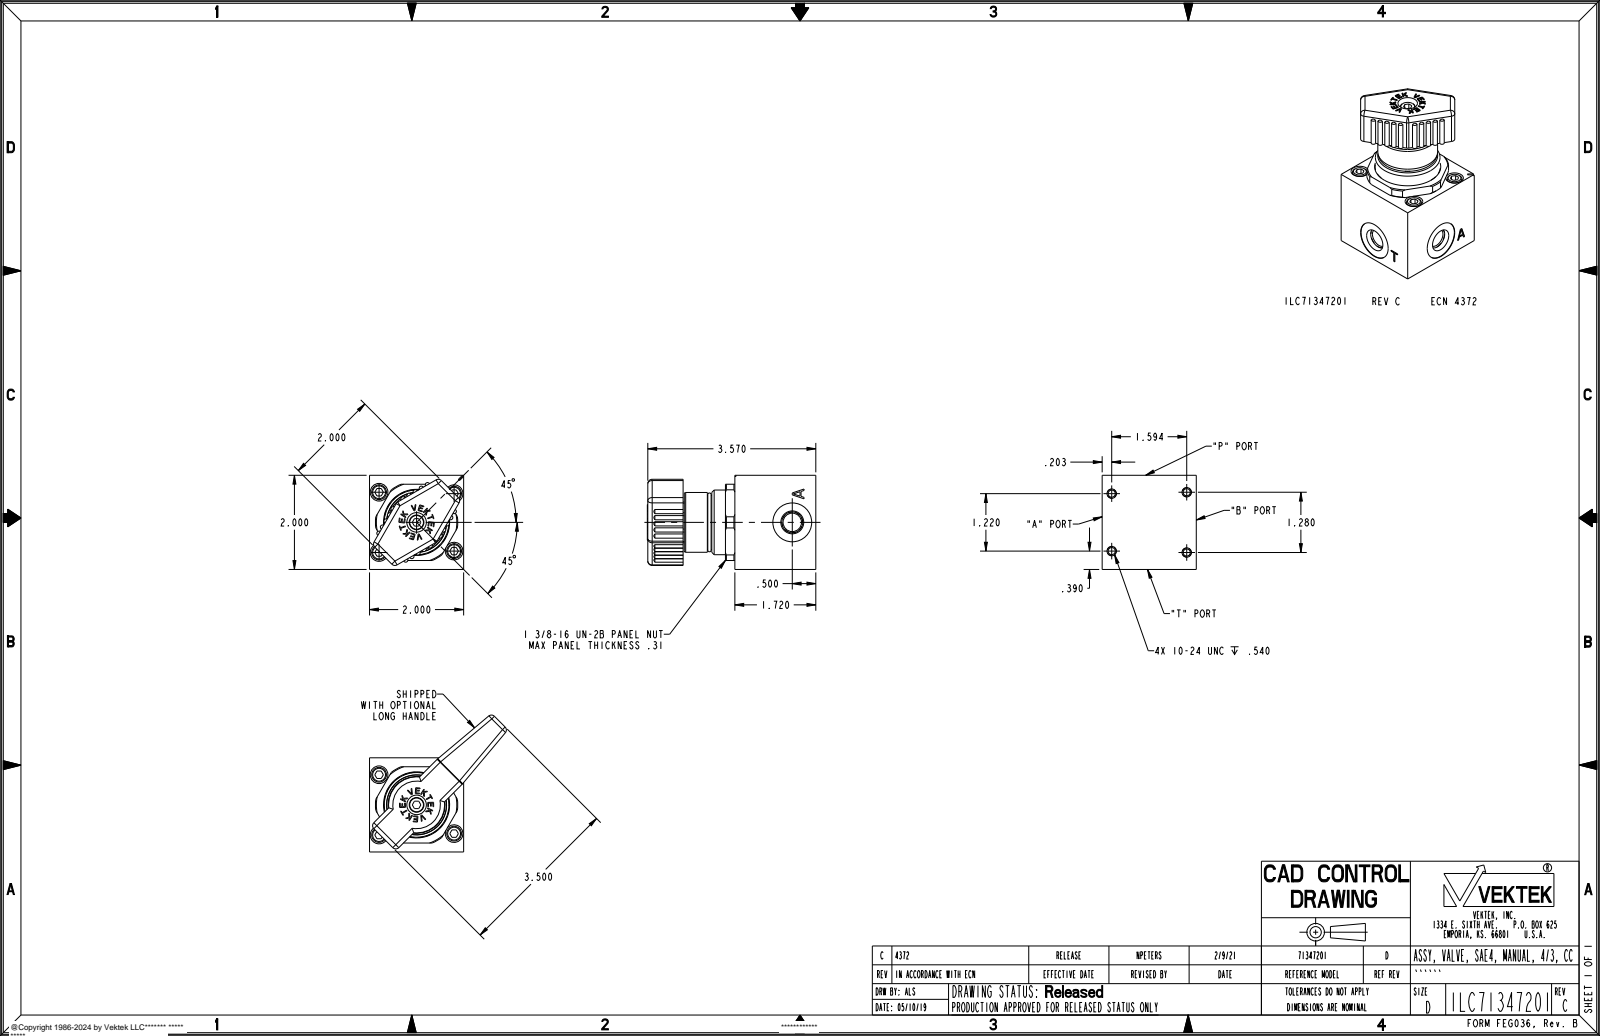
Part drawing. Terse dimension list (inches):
name: ILC71347201_BODY; ILC71347201_ADAPTER; 85600903; 87114013 (+2 more)
written by: PRO/ENGINEER BY PARAMETRIC TECHNOLOGY CORPORATION, 2013320 (AP203_CONFIGURATION_CONTROLLED_3D_DESIGN_OF_MECHANICAL_PARTS_AND_ASSEMBLIES_MIM_LF)
unit: in
bodies: 6 solids, 1734 faces (1396 planar, 216 cylindrical, 122 other)
size: 3.58 × 2.908 × 2.908
volume: 10.12 in³; area: 75.42 in²
holes: 4× ⌀0.151, 4× ⌀0.196, 4× ⌀0.375, 2× ⌀0.199, 2× ⌀0.392, 2× ⌀0.825, 1× ⌀0.203, 1× ⌀0.204, 1× ⌀0.205, 1× ⌀0.415, 1× ⌀0.5, 1× ⌀1.314
bosses: 5× ⌀0.19, 4× ⌀0.313, 2× ⌀0.437, 1× ⌀1.387, 1× ⌀1.373, 1× ⌀1.27, 1× ⌀0.312
rounds: 23× R0.09, 20× R0.048, 12× R0.093, 10× R0.03, 8× R0.045, 8× R0.062, 6× R0.031, 4× R0.12
face distances: 2, 1.72, 0.32, 1.1, 2.82, 0.1, 0.75, 1.42, 3.14, 0.53
hole spacings: 0.437, 1.004, 1.022, 1.594, 2.026, 0.573, 0.589, 0.874
